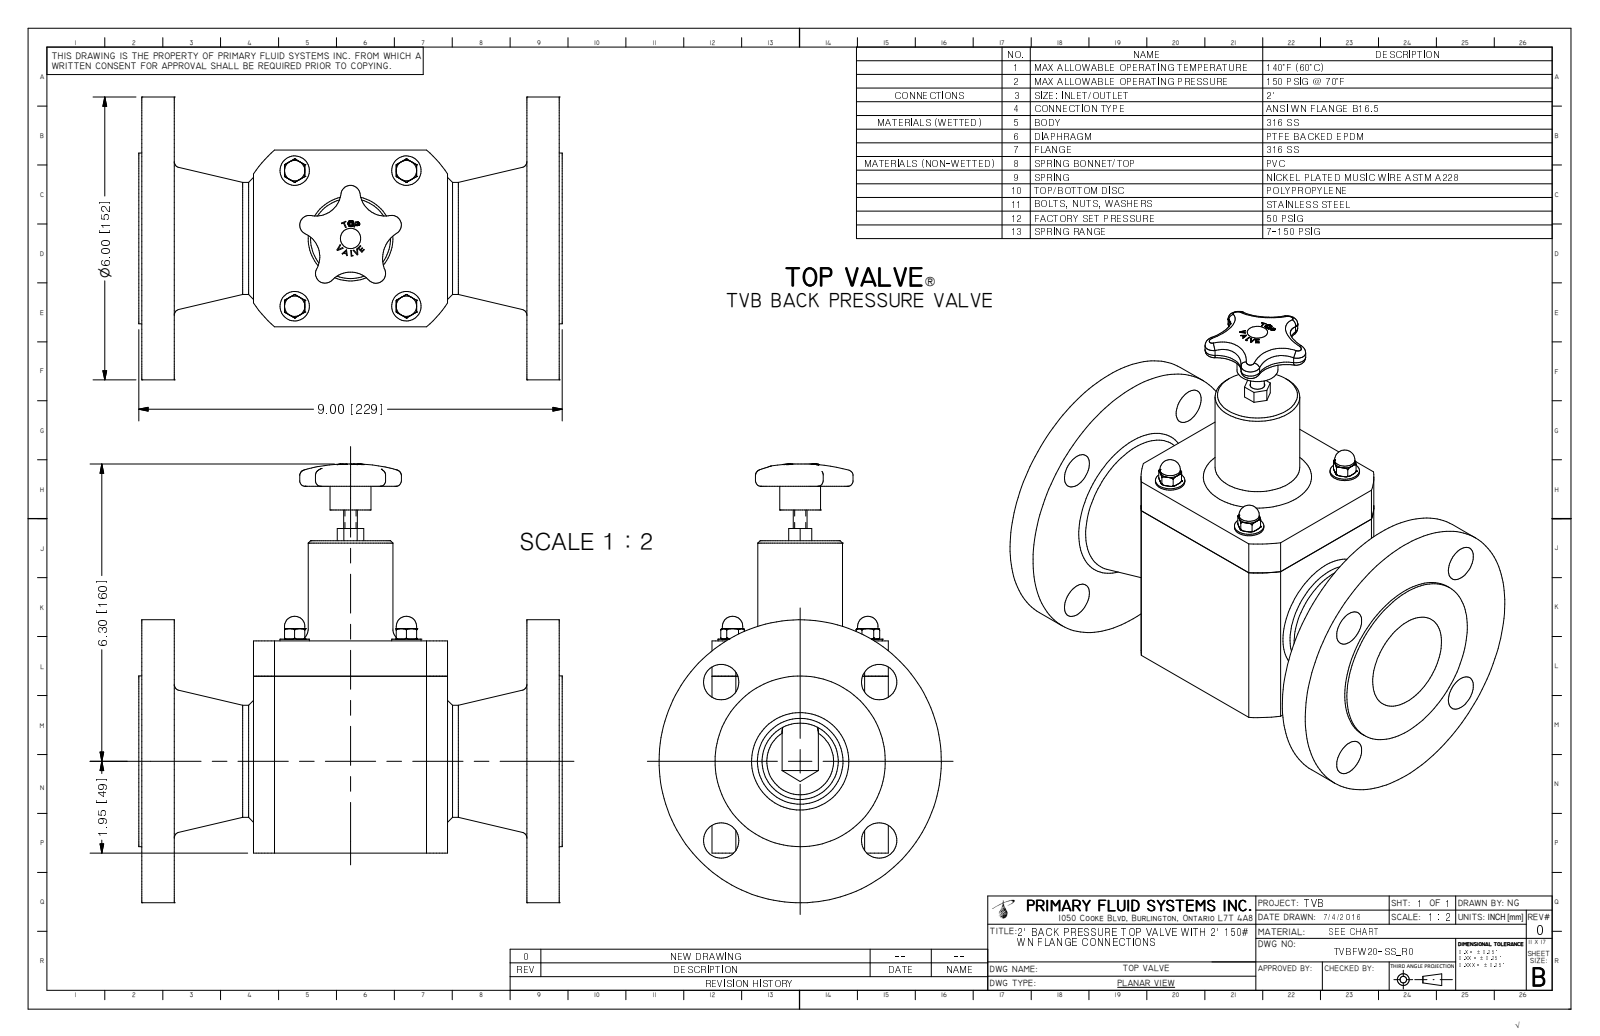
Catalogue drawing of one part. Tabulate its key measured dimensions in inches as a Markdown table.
| quantity | value |
| --- | --- |
| part name | TVBFW20-SS-R0 |
| STEP written by | Autodesk Inventor 2009 (AUTOMOTIVE_DESIGN) |
| units | inches |
| bodies | 1 solid, 361 faces (150 planar, 59 cylindrical, 152 other) |
| overall size | 9.304 × 9 × 6 |
| volume | 114.9 in³ |
| surface area | 306.4 in² |
| round holes (diameter × count) | 0.175 × 4, 0.75 × 4, 2.067 × 1 |
| round bosses / shafts (diameter × count) | 0.625 × 4, 0.433 × 4, 0.375 × 4, 6 × 1, 3.62 × 1, 2.375 × 1, 1.8 × 1, 0.87 × 1 |
| partial cylindrical surfaces (radius × count) | 0.085 × 5, 0.205 × 5, 0.536 × 4, 0.656 × 4, 0.625 × 1, 0.745 × 1, 2.475 × 1 |
| main face-to-face distances | 0.69, 8.185, 7.495, 8.875, 3.75, 2.375, 6.5, 1.685, 5.81, 0.063 |
| hole center spacings | 2.375, 3.359, 2.375, 2.875, 3.729, 4.75 |
